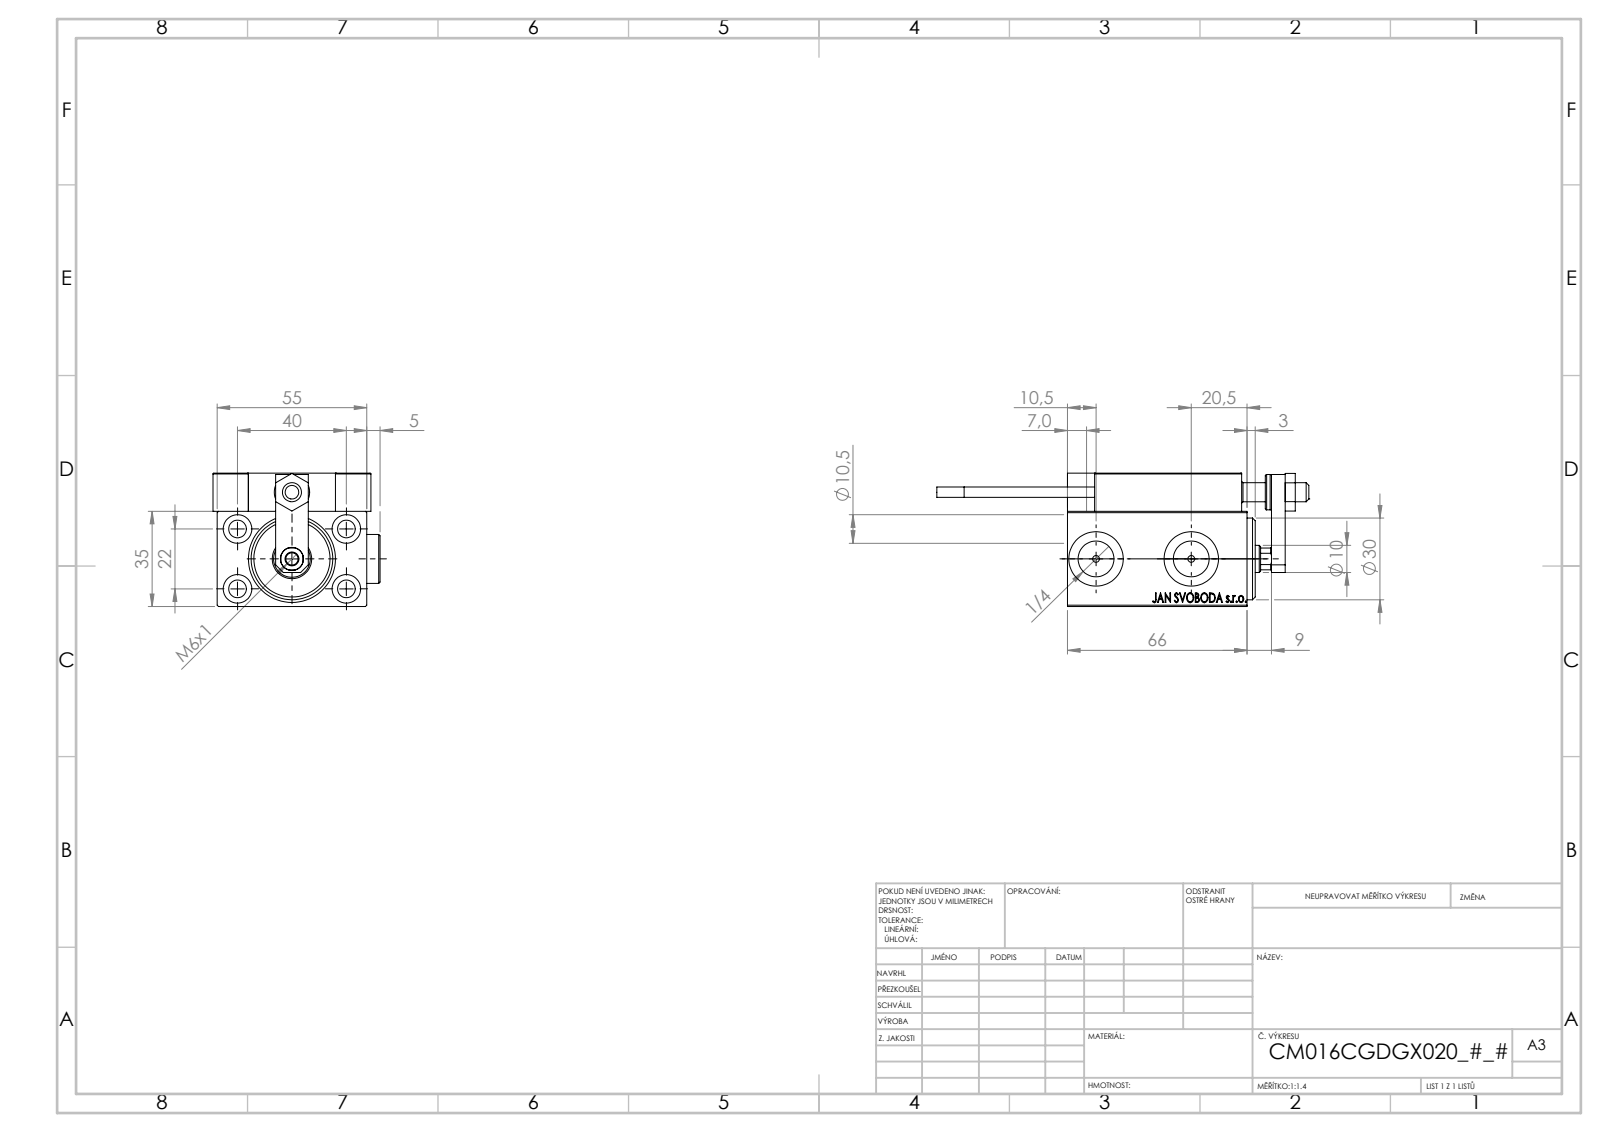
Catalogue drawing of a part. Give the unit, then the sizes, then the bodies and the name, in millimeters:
Units: millimetres
Overall size (bounding box): 136.7 × 61.4 × 49
Round holes (diameter × count): ⌀8 ×5, ⌀3.2 ×4, ⌀4 ×4, ⌀6.5 ×4, ⌀10.5 ×4, ⌀2.5 ×2, ⌀5 ×2, ⌀13.16 ×2, ⌀20 ×2, ⌀4.5 ×1, ⌀7 ×1, ⌀8.5 ×1
Round bosses / shafts (diameter × count): ⌀18 ×2, ⌀5 ×2, ⌀3.8 ×2, ⌀13 ×1, ⌀11 ×1
Partial cylindrical surfaces — rounded edges, fillets, slot ends (radius × count): R0.3 ×28, R3 ×2, R4.5 ×1
Main face-to-face distances: 35, 5, 14, 49, 7, 10, 3, 1.5, 54, 55
Hole centre spacings: 22.83, 11.37, 18.11, 20, 22, 24.13, 28.43, 29.59
Volume: 151 823 mm³ · Surface area: 56 370 mm²
Bodies: 25 solids, 1339 faces (595 planar, 206 cylindrical, 538 other)
Part name (STEP PRODUCT): V450CM_C_Body; SWITCH X; ZARAZKA; V450CM_C_VCP (+8 more)
STEP written by: SolidWorks 2019 (CONFIG_CONTROL_DESIGN)
